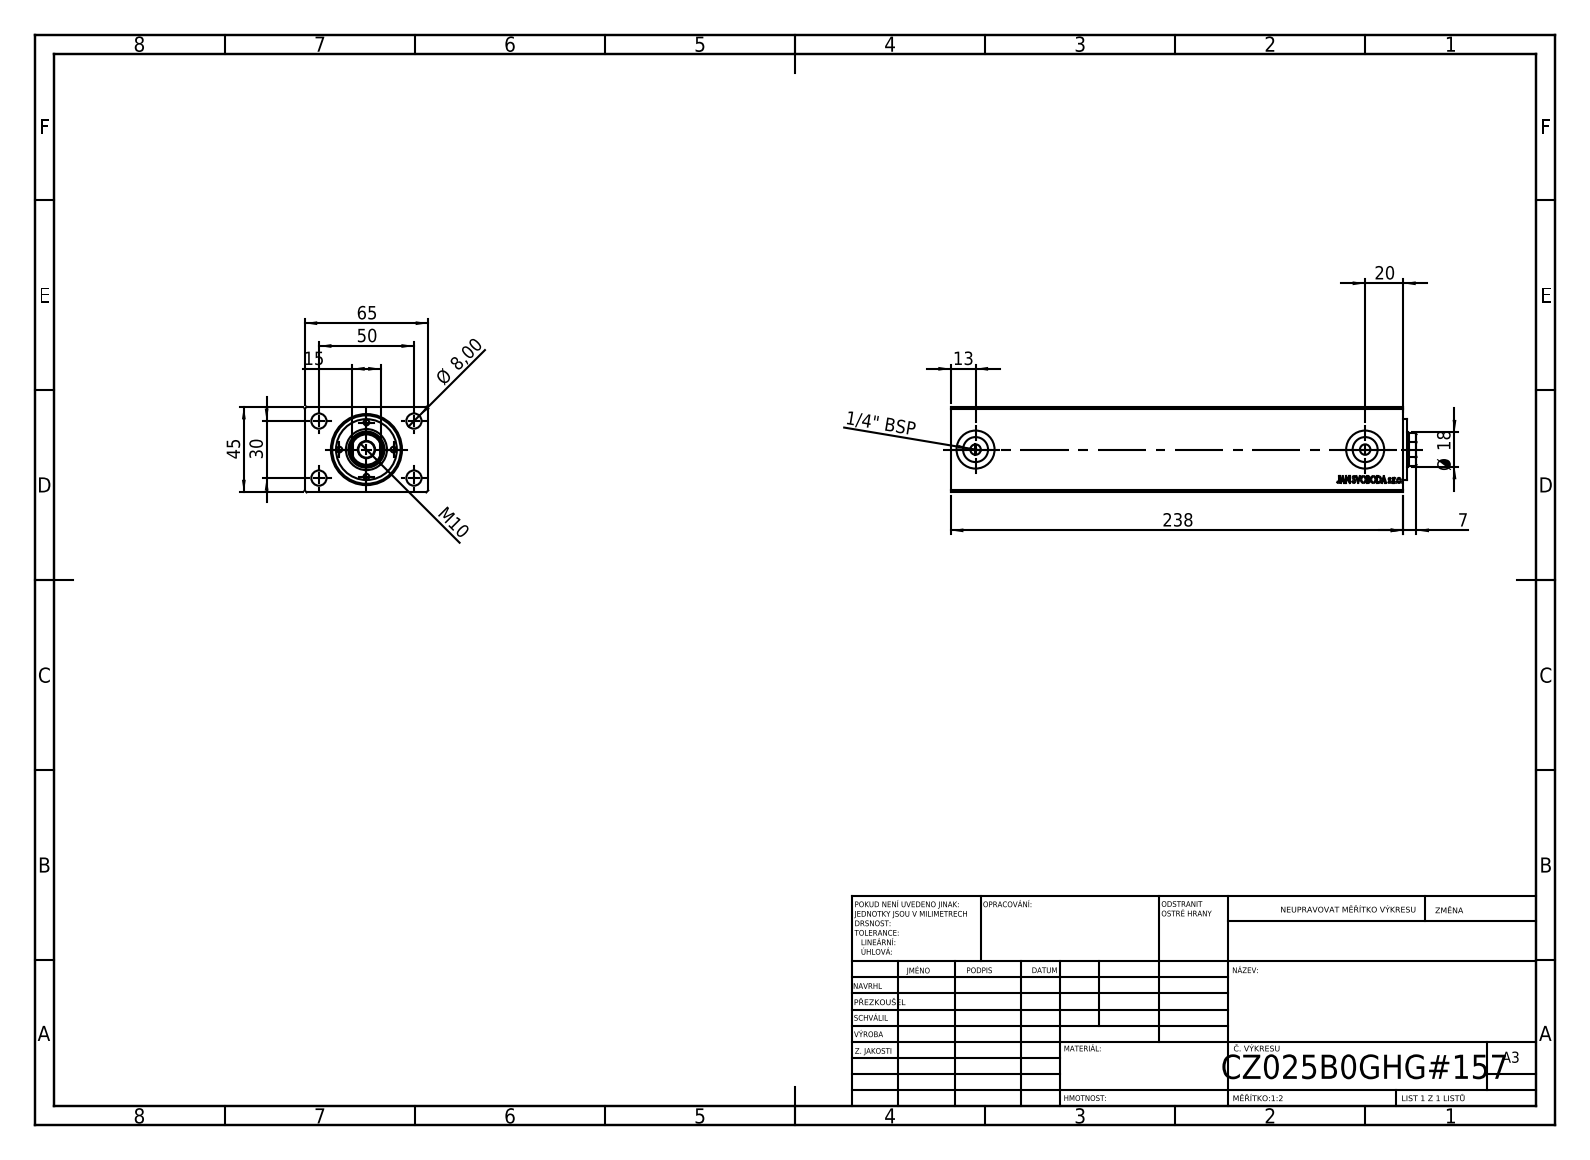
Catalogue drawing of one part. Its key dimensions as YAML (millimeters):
part_name: "V500CZ; V500CZ_B_VC"
step_written_by: "SolidWorks 2019 (CONFIG_CONTROL_DESIGN)"
units: millimeters
bodies: {solids: 3, faces: 873, planar: 399, cylindrical: 58, other: 416}
overall_size: [245, 65, 45]
volume: 644300
surface_area: 100486
round_holes:
  - {diameter: 3, count: 4}
  - {diameter: 8, count: 4}
  - {diameter: 5.5, count: 2}
  - {diameter: 13.16, count: 2}
  - {diameter: 20, count: 2}
  - {diameter: 8.5, count: 1}
  - {diameter: 18, count: 1}
  - {diameter: 19, count: 1}
  - {diameter: 25, count: 1}
  - {diameter: 36, count: 1}
round_bosses_or_shafts:
  - {diameter: 32, count: 1}
partial_cylinders:
  - {radius: 8.5, count: 1}
face_to_face_distances: [45, 65, 238, 7, 237.8, 225.2, 12.6, 12.8, 1.8, 5.2]
hole_center_spacings: [14.25, 18.45, 20.15, 25.01, 29.15, 38.48, 42.02, 28.5]
